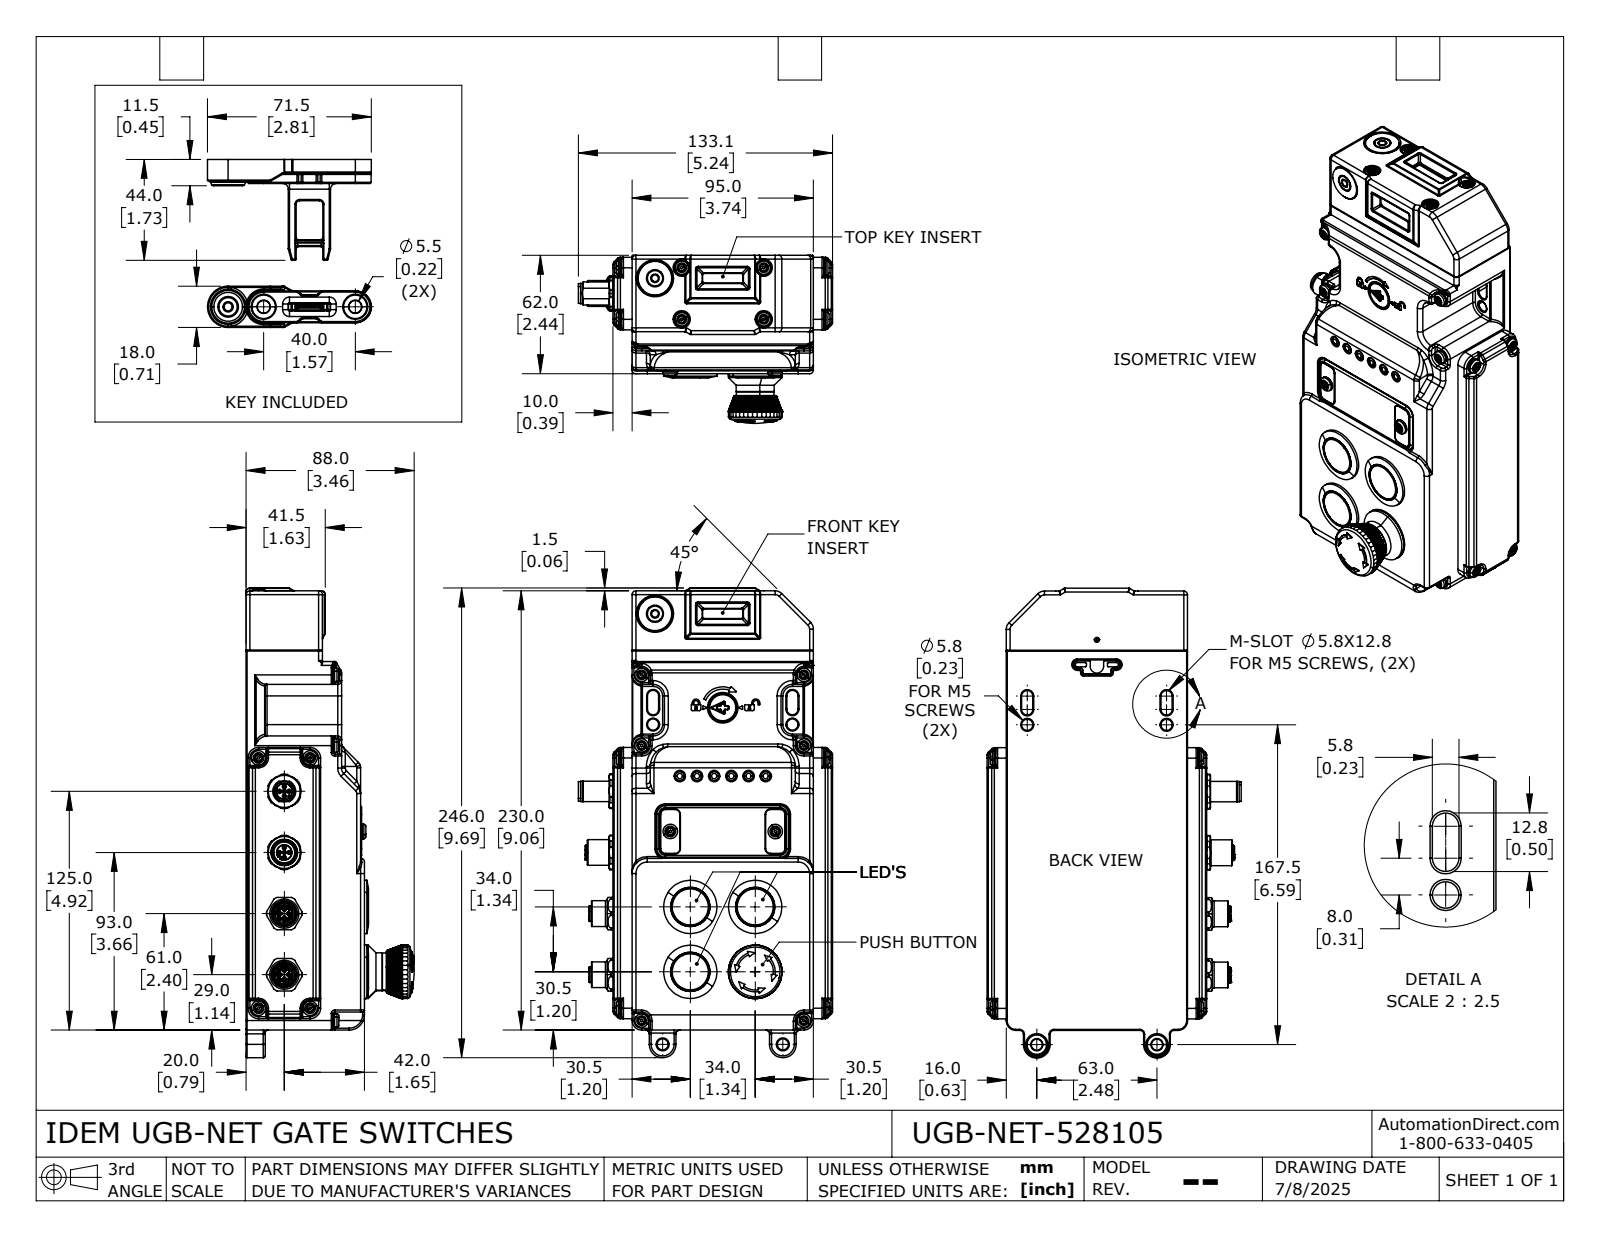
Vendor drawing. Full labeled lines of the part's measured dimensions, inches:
Part name (STEP PRODUCT): UGB-NET-528105
STEP written by: SolidWorks 2024 (AUTOMOTIVE_DESIGN)
Units: inches
Bodies: 7 solids, 4885 faces (1412 planar, 1813 cylindrical, 1660 other)
Overall size (bounding box): 10.217 × 5.24 × 3.465
Volume: 78.29 in³ · Surface area: 203.1 in²
Round holes (diameter × count): ⌀0.157 ×14, ⌀0.177 ×14, ⌀0.049 ×8, ⌀0.077 ×8, ⌀0.315 ×8, ⌀0.087 ×7, ⌀0.098 ×6, ⌀0.197 ×6, ⌀0.043 ×5, ⌀0.13 ×4, ⌀0.165 ×4, ⌀0.217 ×4
Round bosses / shafts (diameter × count): ⌀0.051 ×16, ⌀0.138 ×12, ⌀0.276 ×10, ⌀0.189 ×8, ⌀0.039 ×7, ⌀0.299 ×6, ⌀0.244 ×6, ⌀0.079 ×5
Partial cylindrical surfaces — rounded edges, fillets, slot ends (radius × count): R0.039 ×228, R0.02 ×192, R0.008 ×129, R0.079 ×66, R0.012 ×58, R0.031 ×47, R0.016 ×14, R0.098 ×12
Main face-to-face distances: 0.394, 4.134, 3.74, 2.441, 0.098, 0.492, 3.642, 4.035, 0.472, 1.535
Hole centre spacings: 0.098, 0.139, 0.197, 1.063, 1.264, 1.26, 2.52, 2.522
